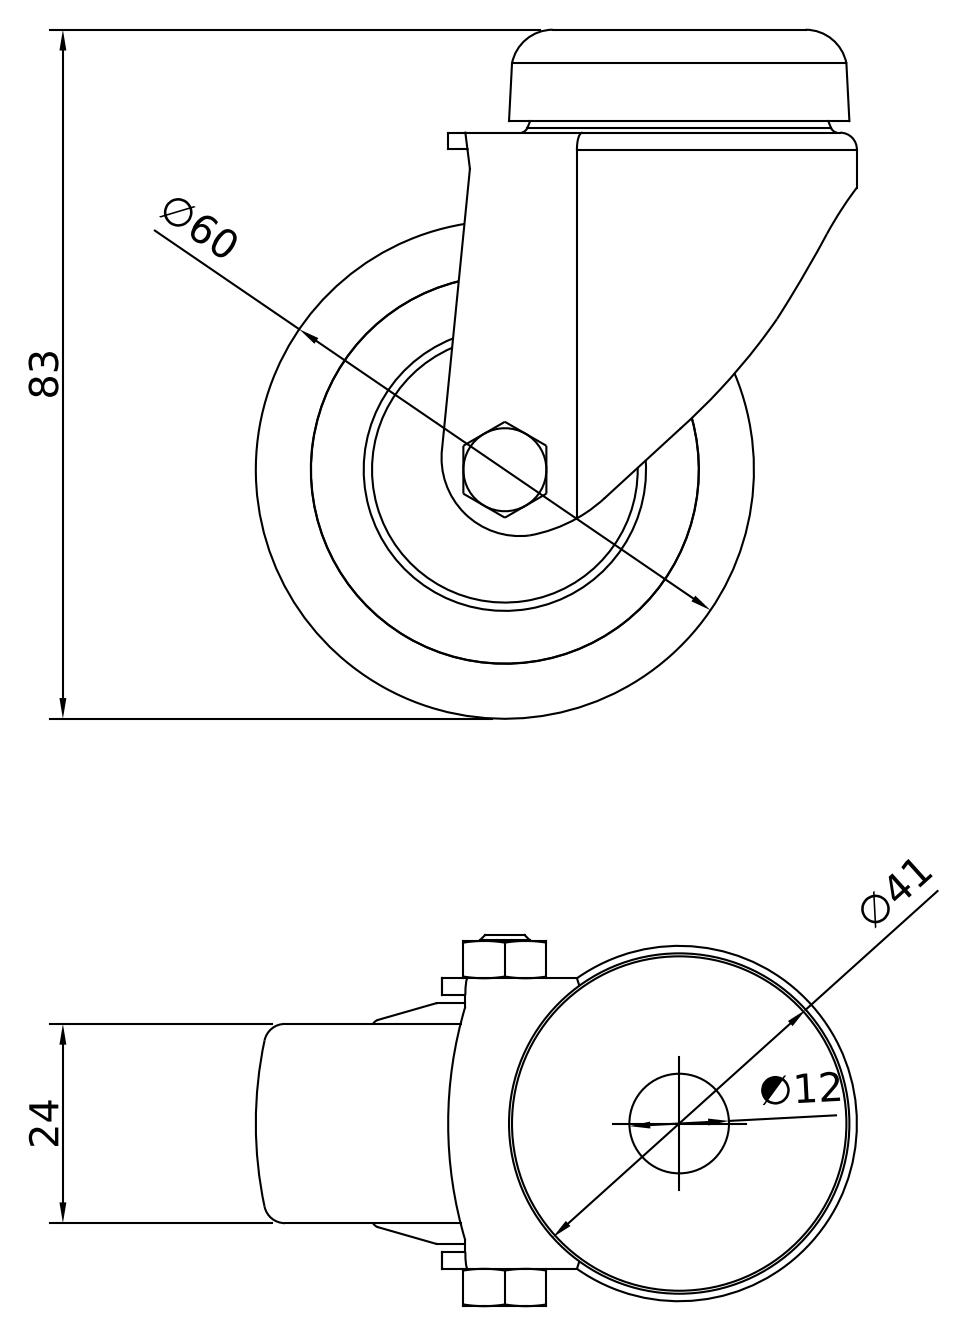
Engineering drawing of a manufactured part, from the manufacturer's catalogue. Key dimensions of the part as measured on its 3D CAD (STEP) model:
Part name (STEP PRODUCT): CRUST0000019; 440000025291; 440000025292; 440000025293 (+3 more)
STEP written by: Autodesk Inventor 2022 (AUTOMOTIVE_DESIGN)
Units: millimetres
Bodies: 7 solids, 156 faces (54 planar, 39 cylindrical, 63 other)
Overall size (bounding box): 83 × 72.4 × 44.7
Volume: 78 441 mm³ · Surface area: 32 715 mm²
Round holes (diameter × count): ⌀4.92 ×1, ⌀6 ×1, ⌀8 ×1, ⌀12 ×1, ⌀31 ×1, ⌀34 ×1, ⌀46.74 ×1
Round bosses / shafts (diameter × count): ⌀46.7 ×1, ⌀33 ×1, ⌀32 ×1, ⌀7.9 ×1, ⌀5.9 ×1
Partial cylindrical surfaces — rounded edges, fillets, slot ends (radius × count): R0.5 ×2, R2 ×2, R9.42 ×1, R18.1 ×1, R19.4 ×1, R21.4 ×1, R45.36 ×1, R49.05 ×1
Main face-to-face distances: 2, 29.5, 3.5, 24, 5.5, 27.5, 33, 10, 35, 31
